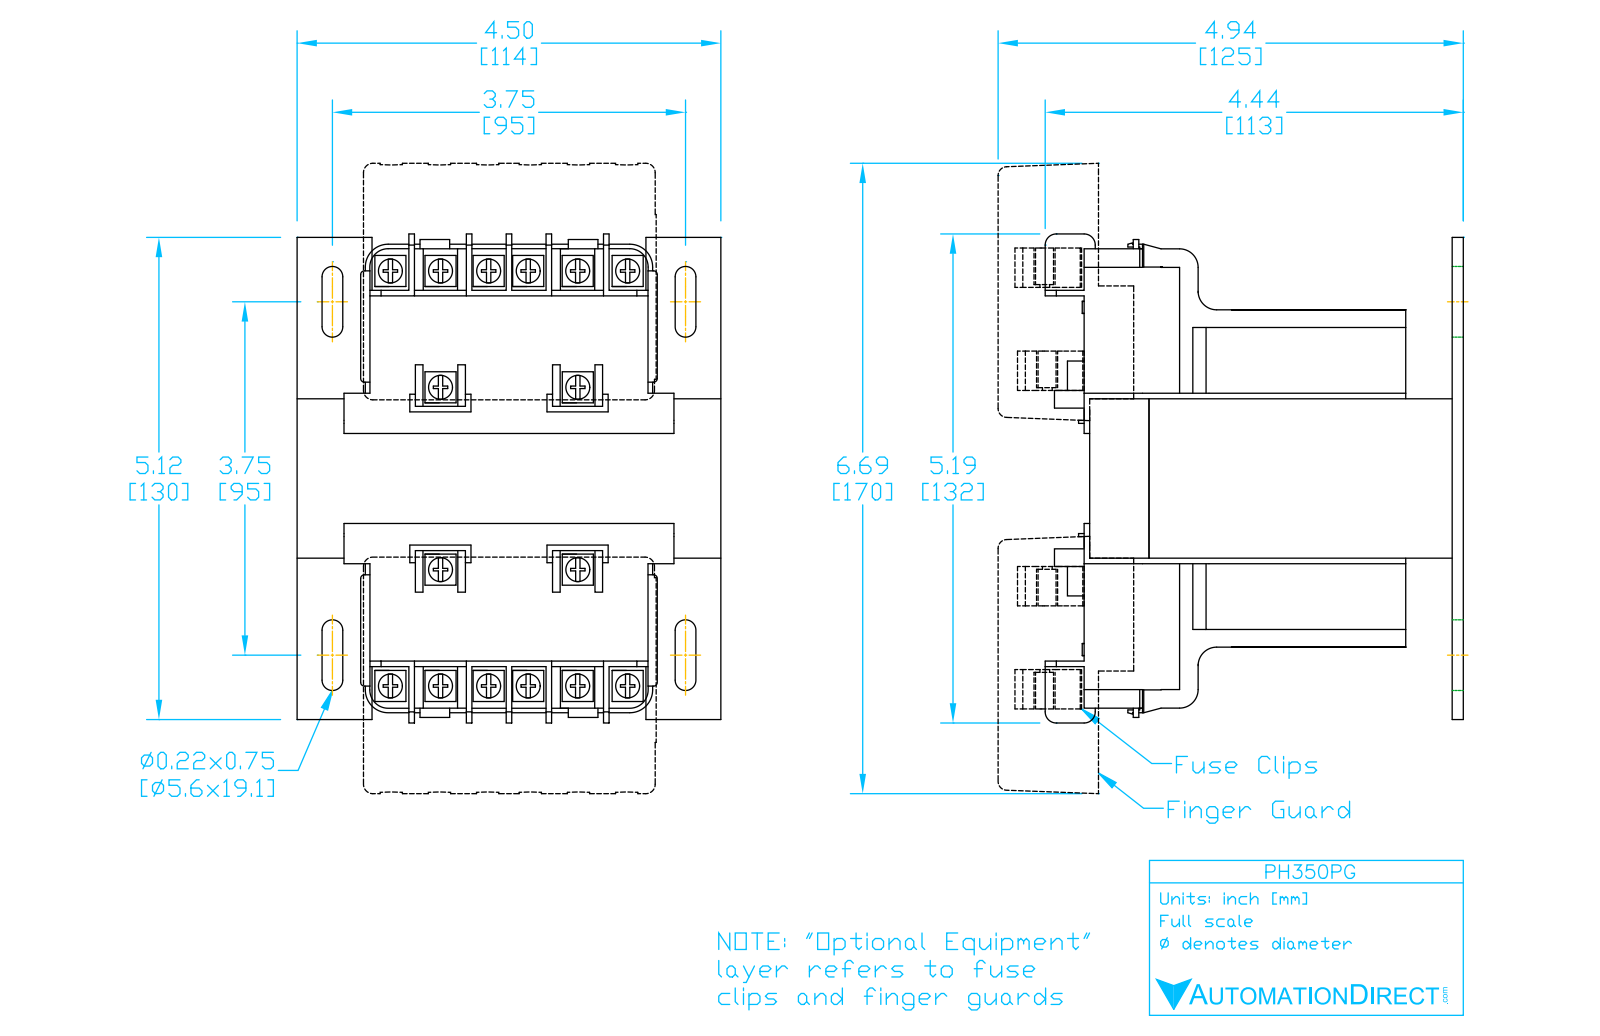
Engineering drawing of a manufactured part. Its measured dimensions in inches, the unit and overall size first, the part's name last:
Units: inches
Overall size (bounding box): 5.075 × 4.5 × 4.331
Round holes (diameter × count): ⌀0.157 ×8
Partial cylindrical surfaces — rounded edges, fillets, slot ends (radius × count): R0.039 ×90, R0.197 ×18, R0.11 ×8, R0.1 ×4, R0.243 ×4
Main face-to-face distances: 1.575, 3.858, 0.187, 2.992, 3.179, 4.213, 1.22, 1.033, 0.63, 0.472
Hole centre spacings: 3.75, 3.991, 0.383, 1.367, 3.769, 0.984, 3.877, 4.138
Volume: 62.25 in³ · Surface area: 215 in²
Bodies: 8 solids, 646 faces (374 planar, 194 cylindrical, 78 other)
Part name (STEP PRODUCT): PH350PG
STEP written by: SolidWorks 2017 (AUTOMOTIVE_DESIGN)
